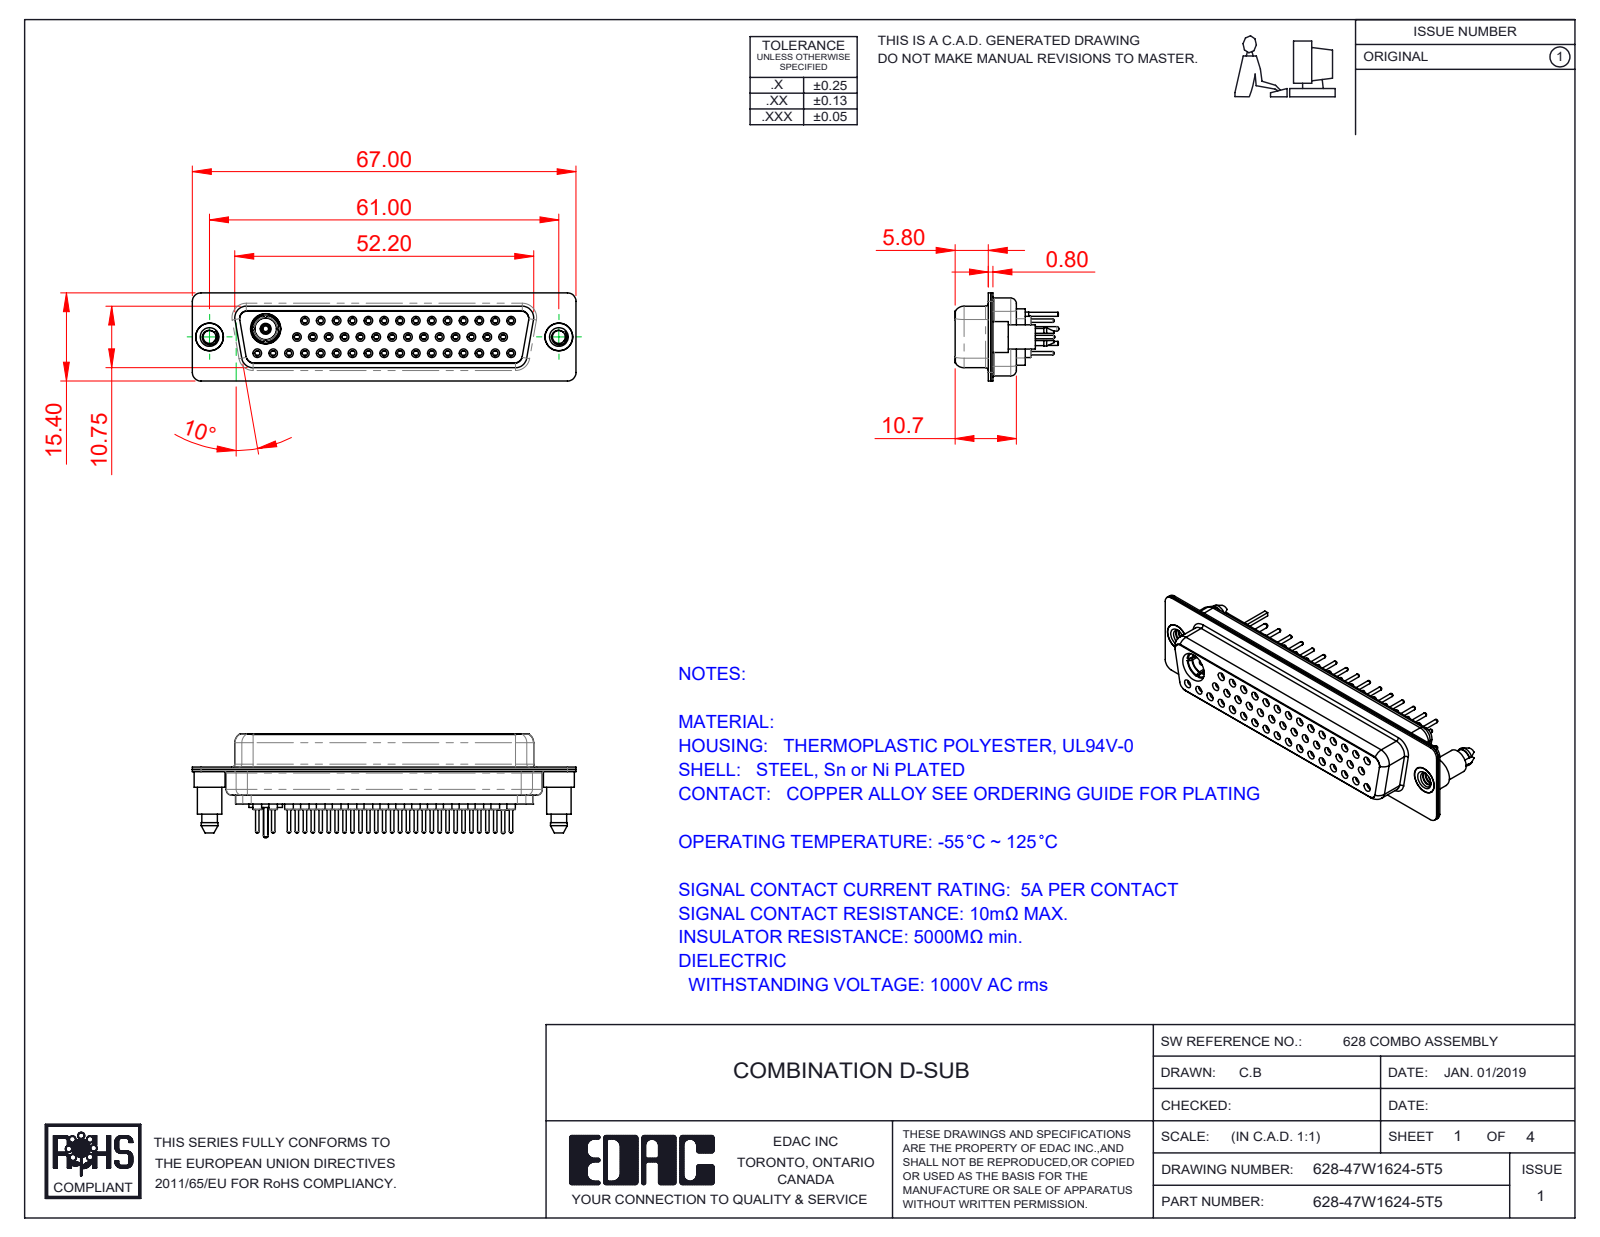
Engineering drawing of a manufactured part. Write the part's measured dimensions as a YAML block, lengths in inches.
part_name: "628-47W1624-5T5; 628Combo Contact Row 3_24; Co-Ax Plug Assy_St; Locking Collar (+8 more)"
step_written_by: "SolidWorks 2016 (CONFIG_CONTROL_DESIGN)"
units: inches
bodies: {solids: 55, faces: 2973, planar: 827, cylindrical: 1080, other: 1066}
overall_size: [2.638, 0.715, 0.606]
volume: 0.438
surface_area: 23.58
round_holes:
  - {diameter: 0.043, count: 47}
  - {diameter: 0.059, count: 46}
  - {diameter: 0.035, count: 45}
  - {diameter: 0.079, count: 45}
  - {diameter: 0.063, count: 31}
  - {diameter: 0.067, count: 14}
  - {diameter: 0.191, count: 3}
  - {diameter: 0.089, count: 2}
  - {diameter: 0.157, count: 2}
  - {diameter: 0.159, count: 2}
  - {diameter: 0.111, count: 1}
  - {diameter: 0.13, count: 1}
round_bosses_or_shafts:
  - {diameter: 0.087, count: 46}
  - {diameter: 0.024, count: 46}
  - {diameter: 0.063, count: 15}
  - {diameter: 0.213, count: 2}
  - {diameter: 0.195, count: 2}
  - {diameter: 0.189, count: 2}
  - {diameter: 0.167, count: 2}
  - {diameter: 0.23, count: 1}
partial_cylinders:
  - {radius: 0.059, count: 18}
  - {radius: 0.053, count: 12}
  - {radius: 0.079, count: 12}
  - {radius: 0.063, count: 10}
  - {radius: 0.01, count: 4}
  - {radius: 0.02, count: 4}
  - {radius: 0.024, count: 4}
  - {radius: 0.026, count: 4}
face_to_face_distances: [0.016, 0.238, 0.254, 0.446, 0.074, 0.482, 0.244, 0.228, 0.407, 0.43]
hole_center_spacings: [0.124, 0.109, 0.218, 0.327, 0.436, 0.545, 0.654, 0.763]
